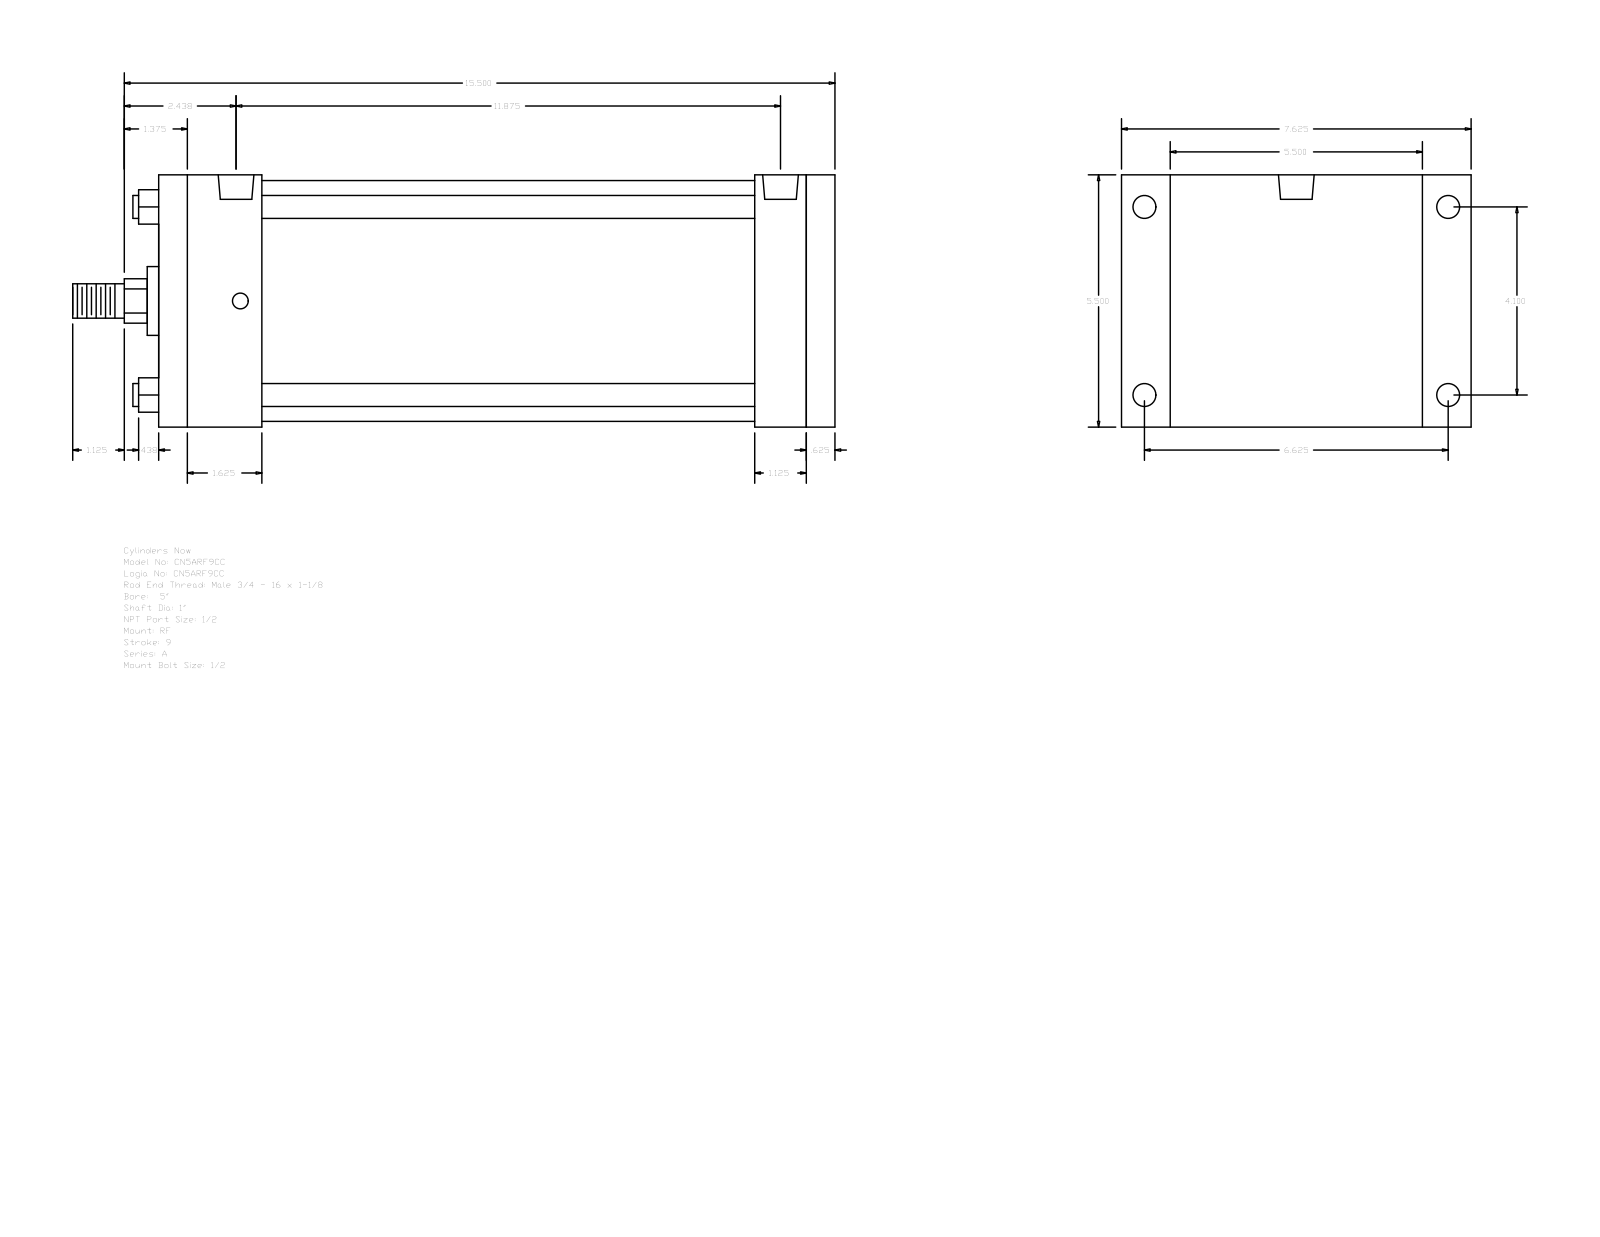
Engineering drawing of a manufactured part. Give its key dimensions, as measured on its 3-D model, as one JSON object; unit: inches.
{"part_name": "A_RF__0500_1", "step_written_by": "GSSL Pune (CONFIG_CONTROL_DESIGN)", "units": "inches", "bodies": {"solids": 0, "faces": 92, "planar": 64, "cylindrical": 28, "other": 0}, "overall_size": [16.625, 7.625, 5.5], "round_holes": [[0.344, 4], [0.5, 4], [0.778, 2]], "round_bosses_or_shafts": [[0.5, 4], [5.25, 1], [1.5, 1], [1, 1], [0.75, 1]], "partial_cylinders_radius": [[0.484, 1]], "face_to_face_distances": [5.5, 14.75, 14.125, 0.625, 1.125, 2.25, 11.875, 12.5, 13, 10.75], "hole_center_spacings": [0.094, 4.1, 6.625, 7.791, 11.687, 11.781, 11.875]}
